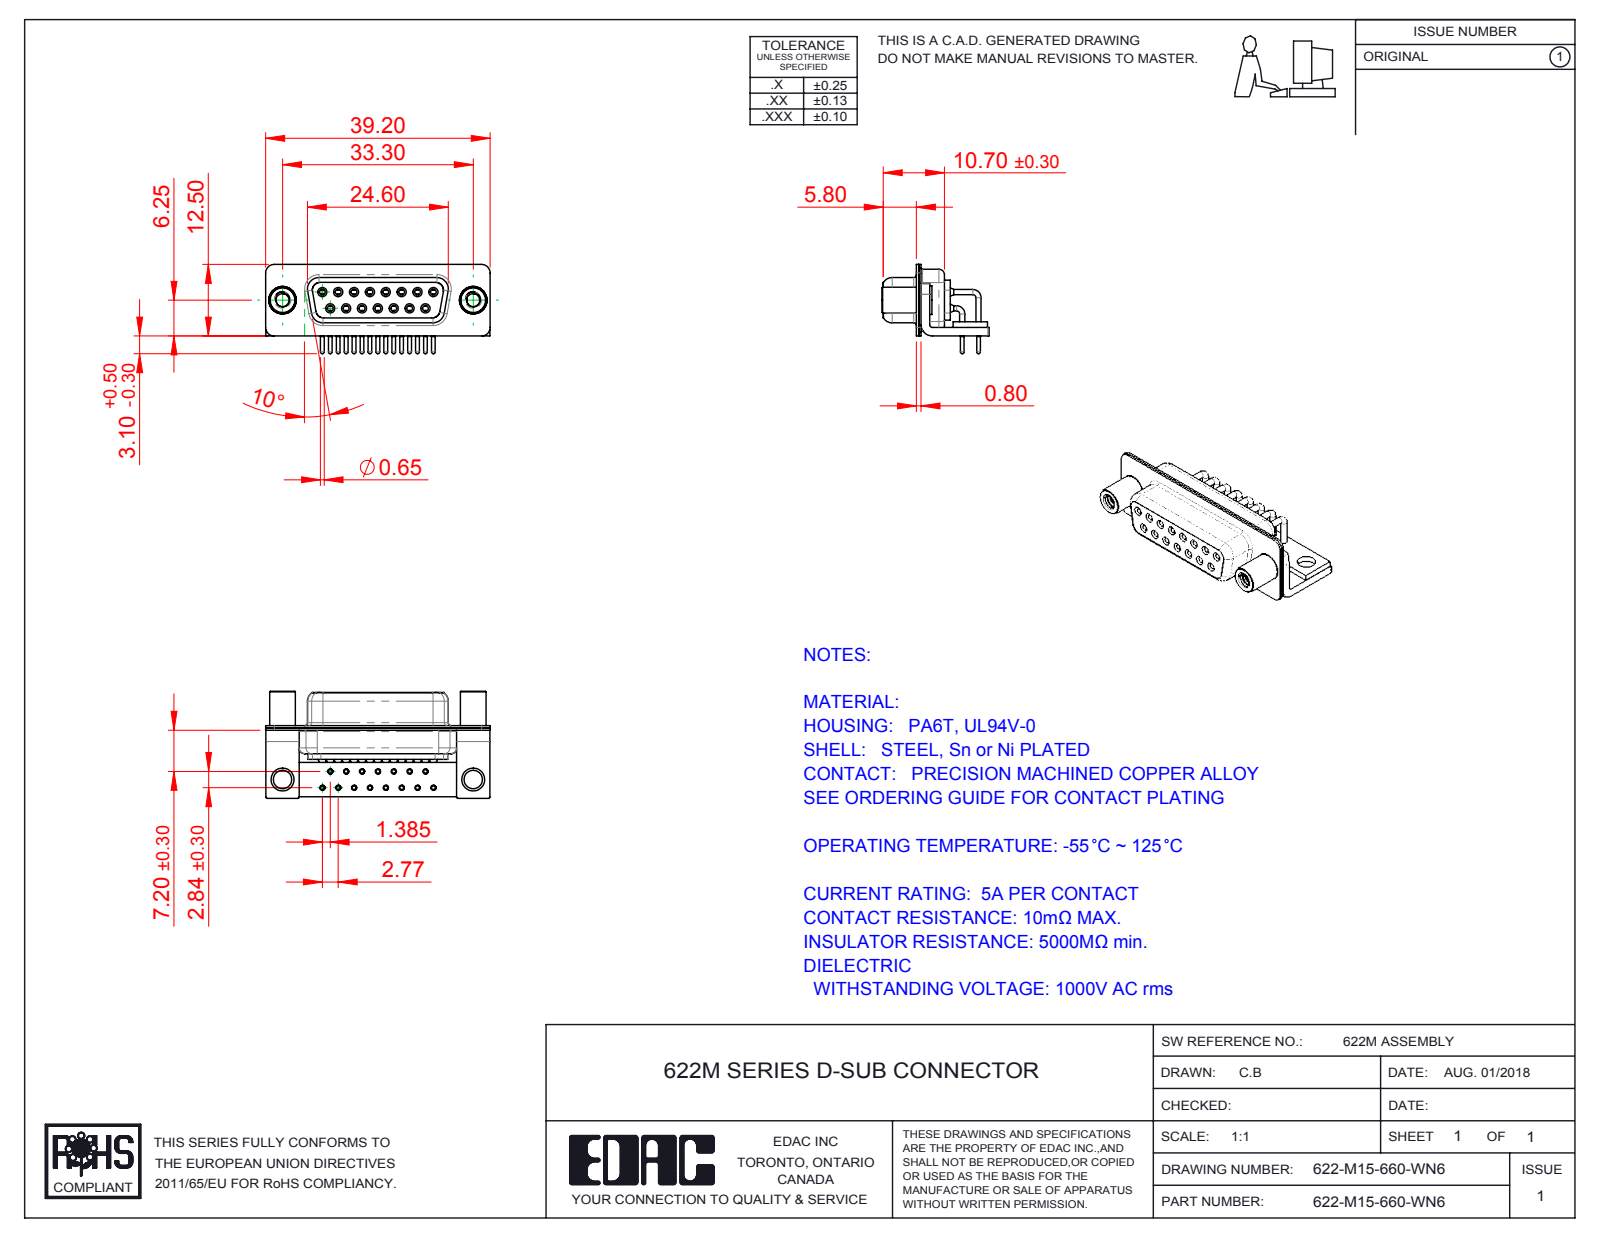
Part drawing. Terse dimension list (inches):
name: 622M Stabilizer Bracket; 622M Contact Row 2; 622M 4-40 Threaded Standoff; 622M Contact Row 1 (+5 more)
written by: SolidWorks 2016 (CONFIG_CONTROL_DESIGN)
unit: in
bodies: 23 solids, 1204 faces (320 planar, 576 cylindrical, 308 other)
size: 1.543 × 0.736 × 0.614
volume: 0.189 in³; area: 12.13 in²
holes: 15× ⌀0.035, 15× ⌀0.039, 15× ⌀0.043, 15× ⌀0.067, 15× ⌀0.071, 15× ⌀0.079, 2× ⌀0.089, 2× ⌀0.126, 2× ⌀0.157, 2× ⌀0.189
bosses: 22× ⌀0.035, 15× ⌀0.063, 15× ⌀0.059, 15× ⌀0.026, 2× ⌀0.197, 2× ⌀0.193, 2× ⌀0.177
rounds: 16× R0.01, 16× R0.059, 13× R0.079, 8× R0.053, 8× R0.063, 5× R0.02, 4× R0.024, 4× R0.026
face distances: 0.016, 0.091, 0.075, 0.031, 0.368, 0.059, 0.039, 0.057, 0.352, 0.033
hole spacings: 0.124, 0.109, 0.218, 0.327, 0.436, 0.198, 0.198, 0.294
